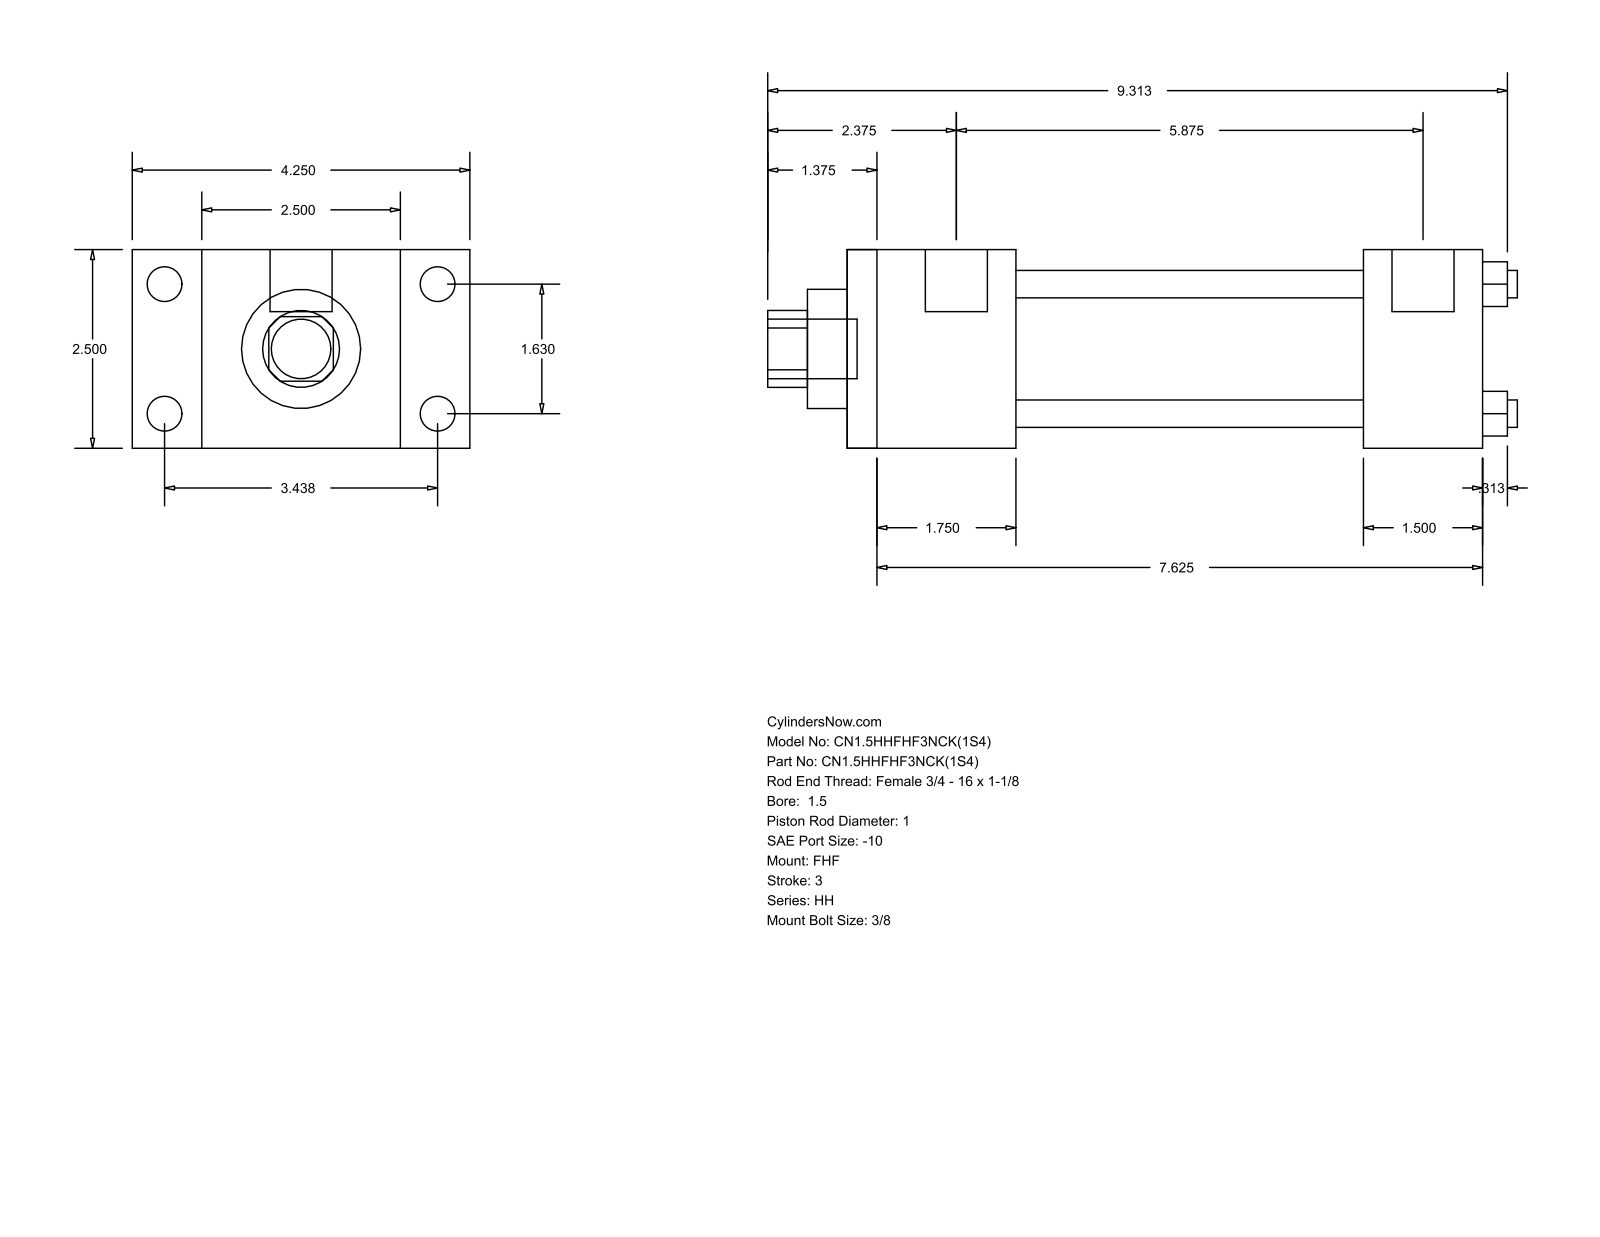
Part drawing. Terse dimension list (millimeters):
name: HH_FHF__0150_1
written by: GSSL Pune (CONFIG_CONTROL_DESIGN)
unit: mm
bodies: 0 solids, 88 faces (60 planar, 28 cylindrical, 0 other)
size: 239.71 × 107.95 × 63.5
holes: 4× ⌀8.76, 1× ⌀25.4, 1× ⌀38.1, 1× ⌀44.45
bosses: 4× ⌀11.13, 4× ⌀5.56, 2× ⌀19.84, 1× ⌀19.05
rounds: 1× R12.29
face distances: 63.5, 22.23, 85.73, 53.98, 107.96, 203.2, 149.22, 165.1, 111.12, 38.1
hole spacings: 29.27, 41.4, 58.55
